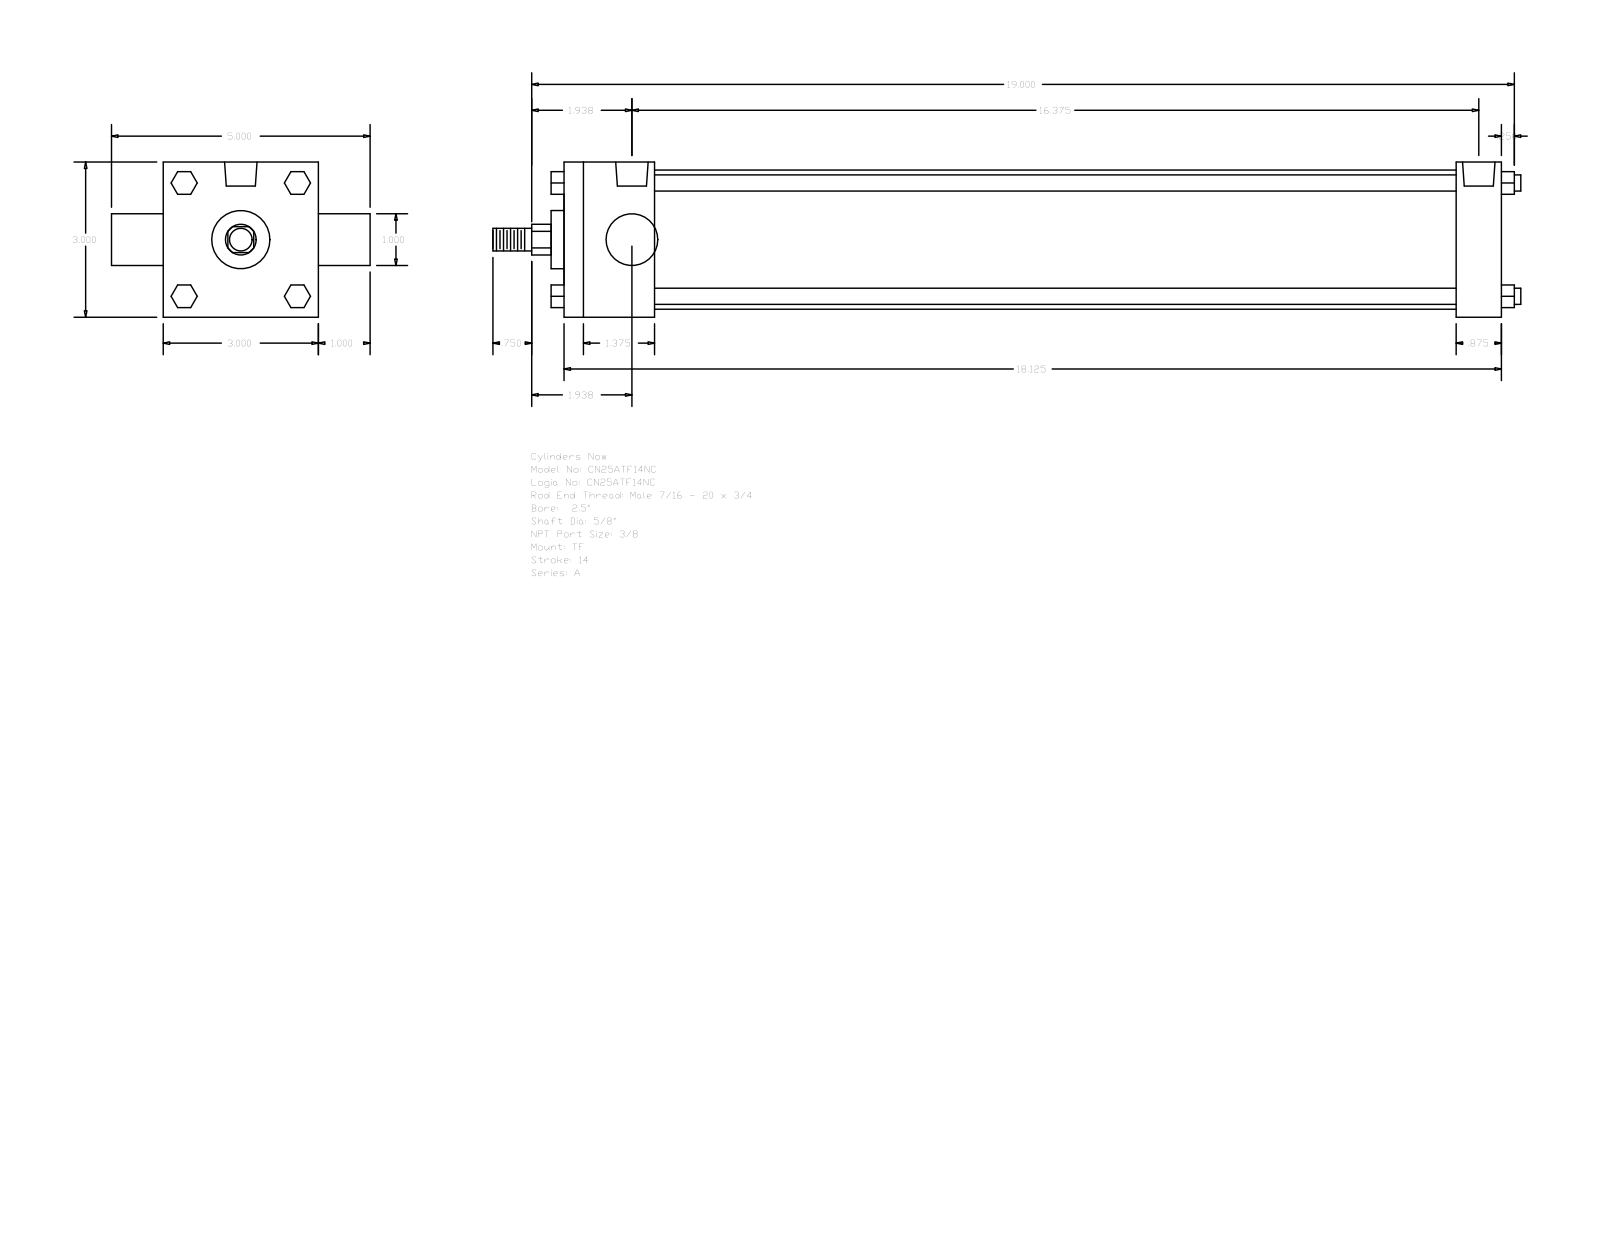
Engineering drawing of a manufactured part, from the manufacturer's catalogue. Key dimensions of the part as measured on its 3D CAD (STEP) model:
Part name (STEP PRODUCT): A_TF__0250_0.625
STEP written by: GSSL Pune (CONFIG_CONTROL_DESIGN)
Units: millimetres
Bodies: 0 solids, 120 faces (92 planar, 28 cylindrical, 0 other)
Overall size (bounding box): 504.82 × 127 × 76.2
Round holes (diameter × count): ⌀5.56 ×3, ⌀15.93 ×2
Round bosses / shafts (diameter × count): ⌀7.94 ×4, ⌀68.33 ×1, ⌀28.57 ×1, ⌀25.4 ×1, ⌀15.88 ×1, ⌀11.11 ×1
Partial cylindrical surfaces — rounded edges, fillets, slot ends (radius × count): R7.54 ×1
Main face-to-face distances: 76.2, 460.37, 44.45, 438.14, 393.69, 415.92, 22.23, 25.4, 101.6, 6.35
Hole centre spacings: 2.38, 418.31, 415.93, 420.69
